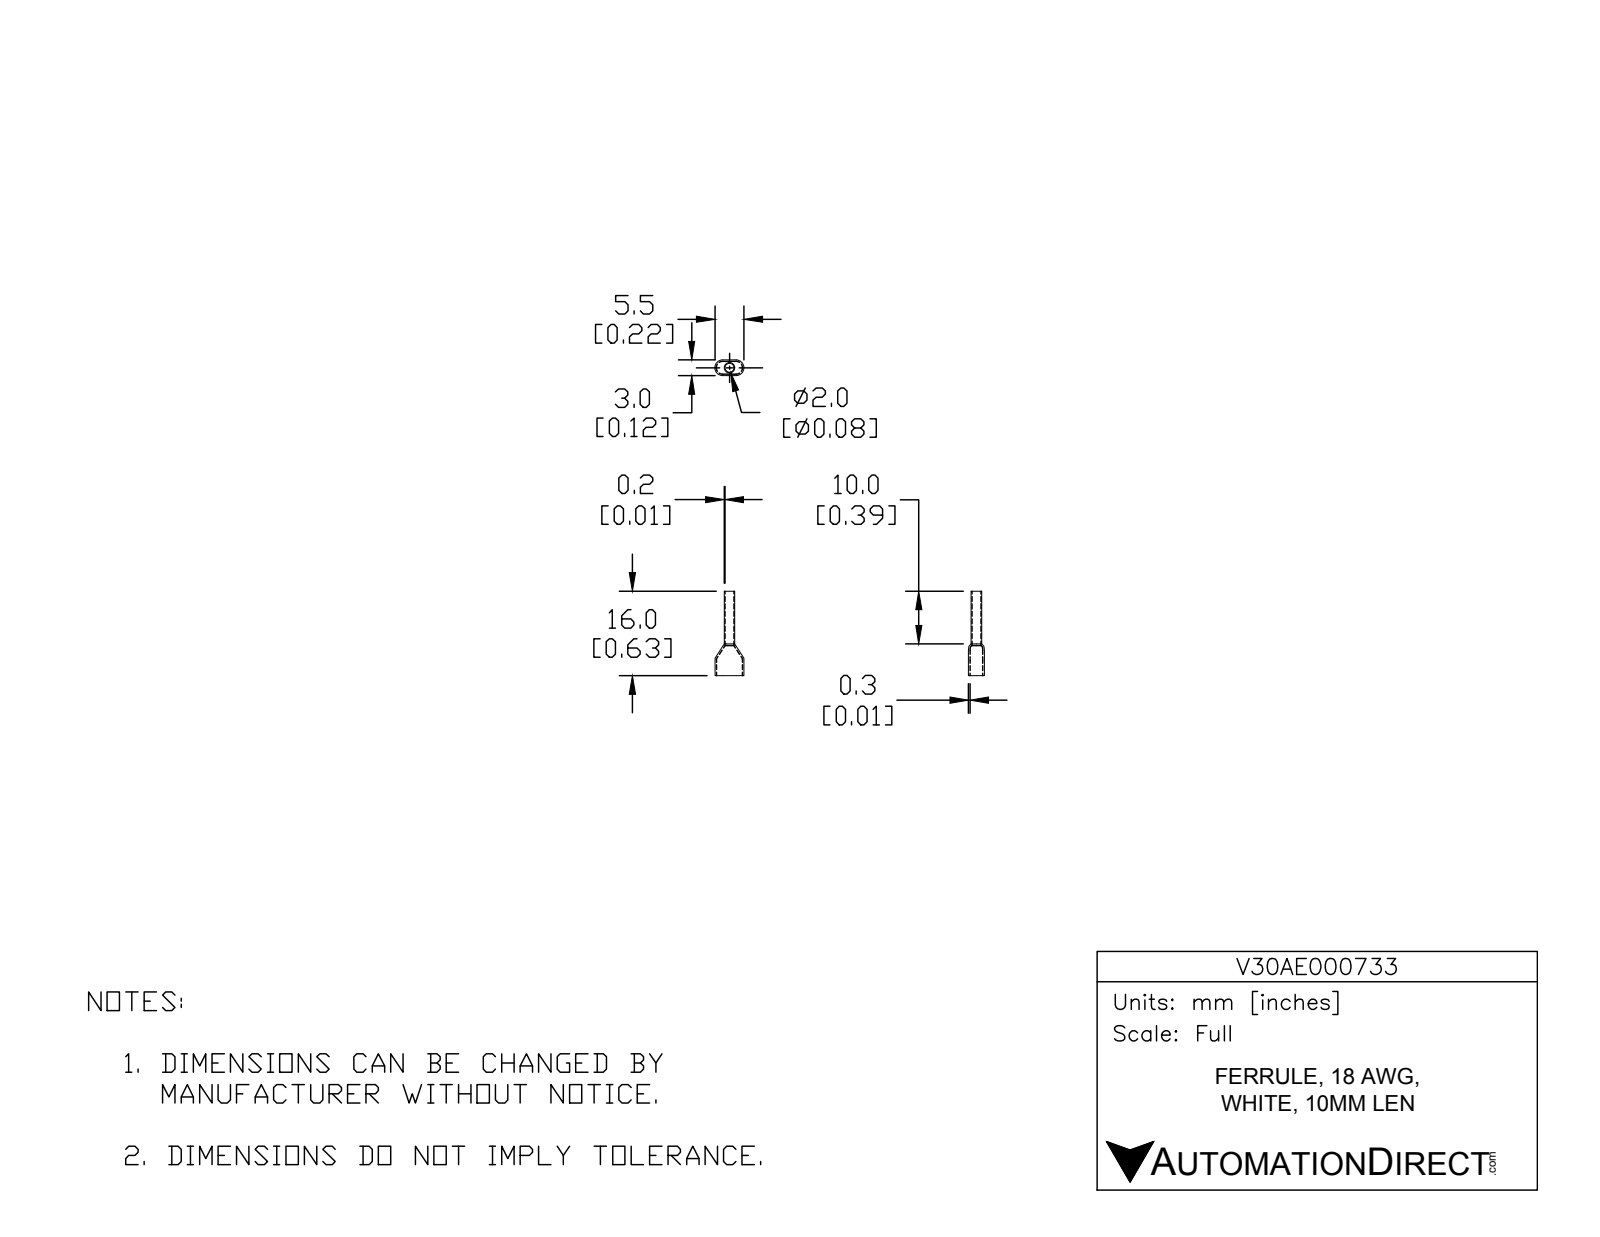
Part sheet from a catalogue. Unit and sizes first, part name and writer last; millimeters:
Units: millimetres
Overall size (bounding box): 16 × 5.5 × 3
Round holes (diameter × count): ⌀1.7 ×1
Round bosses / shafts (diameter × count): ⌀2 ×1
Partial cylindrical surfaces — rounded edges, fillets, slot ends (radius × count): R1.2 ×4, R1.5 ×4
Main face-to-face distances: 2.7, 3, 2.4, 6, 16, 10, 5.7, 10.3
Volume: 30 mm³ · Surface area: 269 mm²
Bodies: 2 solids, 36 faces (14 planar, 22 cylindrical, 0 other)
Part name (STEP PRODUCT): V30AE000733
STEP written by: SolidWorks 2017 (AUTOMOTIVE_DESIGN)
